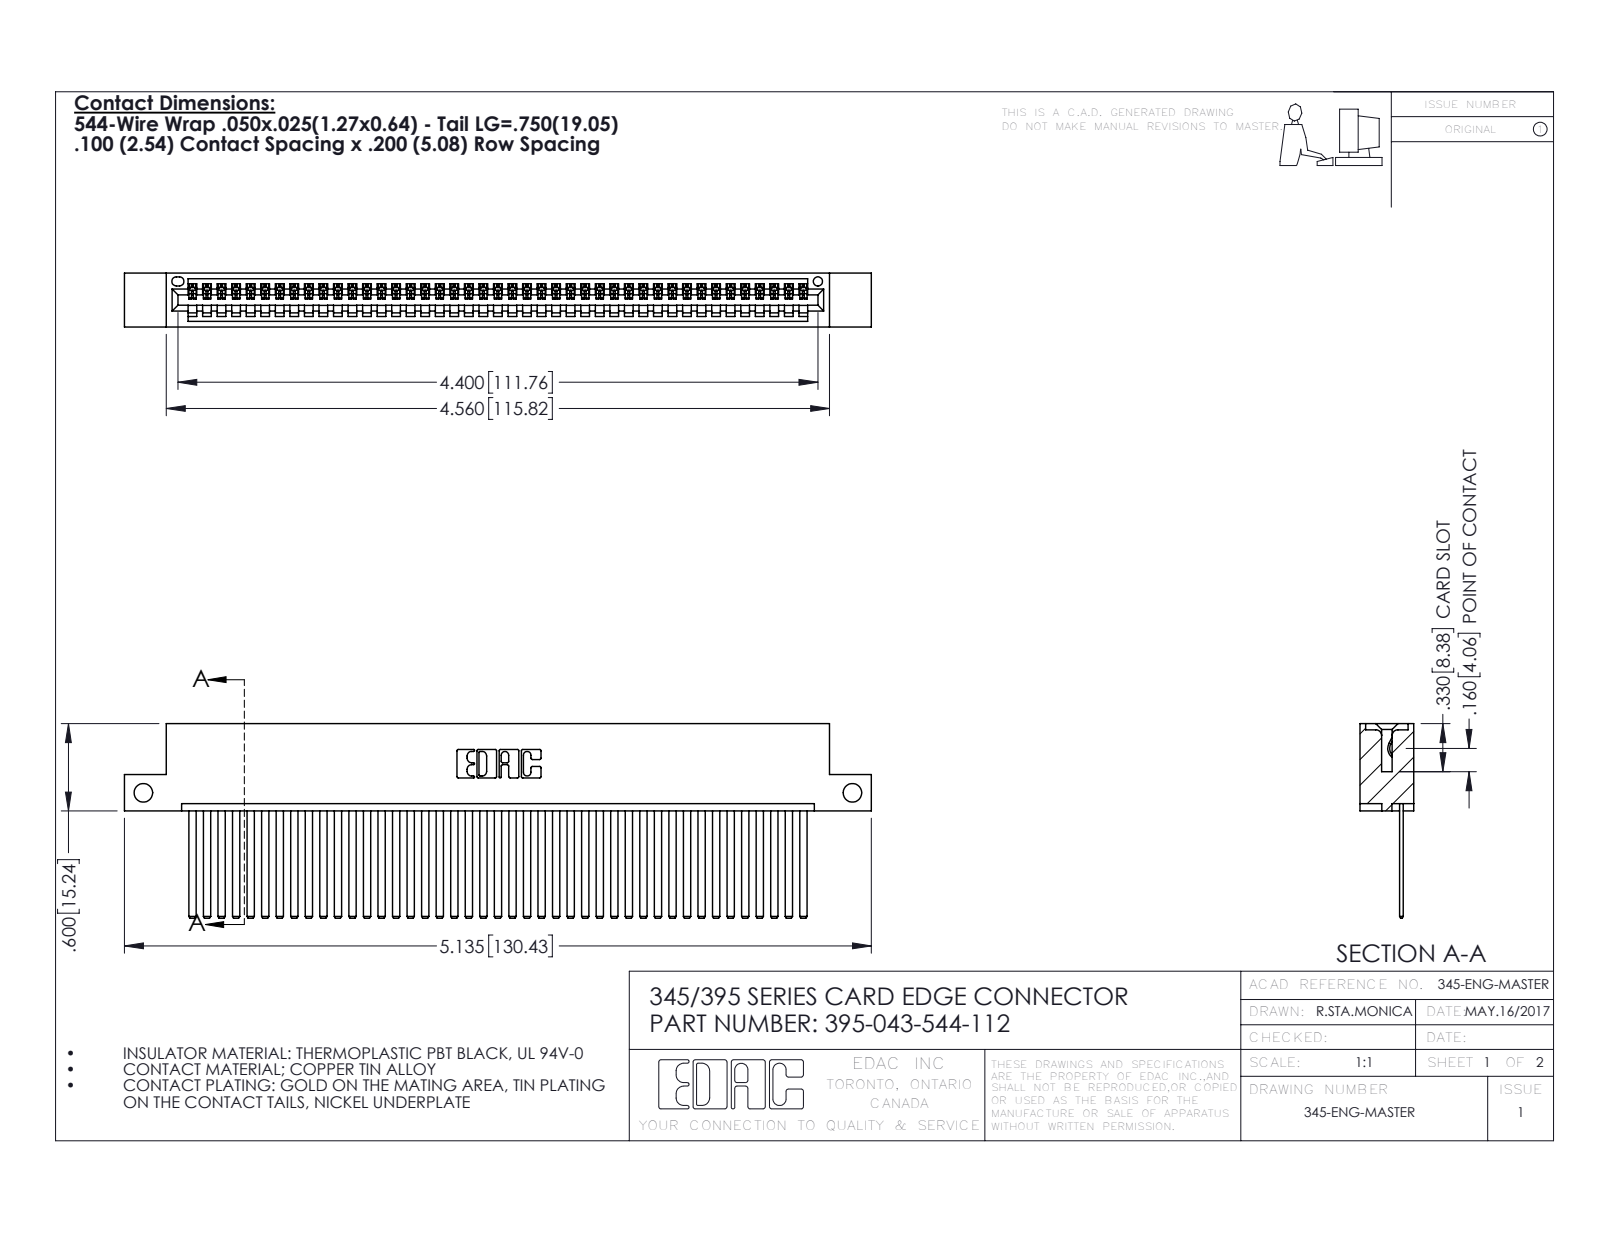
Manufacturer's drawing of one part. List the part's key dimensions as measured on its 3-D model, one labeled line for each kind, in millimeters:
Part name (STEP PRODUCT): 345 Part_Flush Mounting Lugs - Side Mount; 395-043-544-112; 345-292-001_345-293-144
STEP written by: SolidWorks 2016 (CONFIG_CONTROL_DESIGN)
Units: millimetres
Bodies: 44 solids, 2362 faces (1628 planar, 734 cylindrical, 0 other)
Overall size (bounding box): 130.4 × 34 × 9.4
Volume: 12 800 mm³ · Surface area: 18 390 mm²
Round holes (diameter × count): ⌀3.3 ×2, ⌀1.6 ×1
Partial cylindrical surfaces — rounded edges, fillets, slot ends (radius × count): R0.2 ×86, R0.3 ×22, R0.2 ×6, R0.8 ×6, R0.7 ×3, R0.8 ×2, R1 ×2, R0.4 ×1
Main face-to-face distances: 1.8, 7.6, 0.6, 2.5, 6.9, 9.4, 5.1, 5.7, 3.8, 1.8
Hole centre spacings: 123.8
